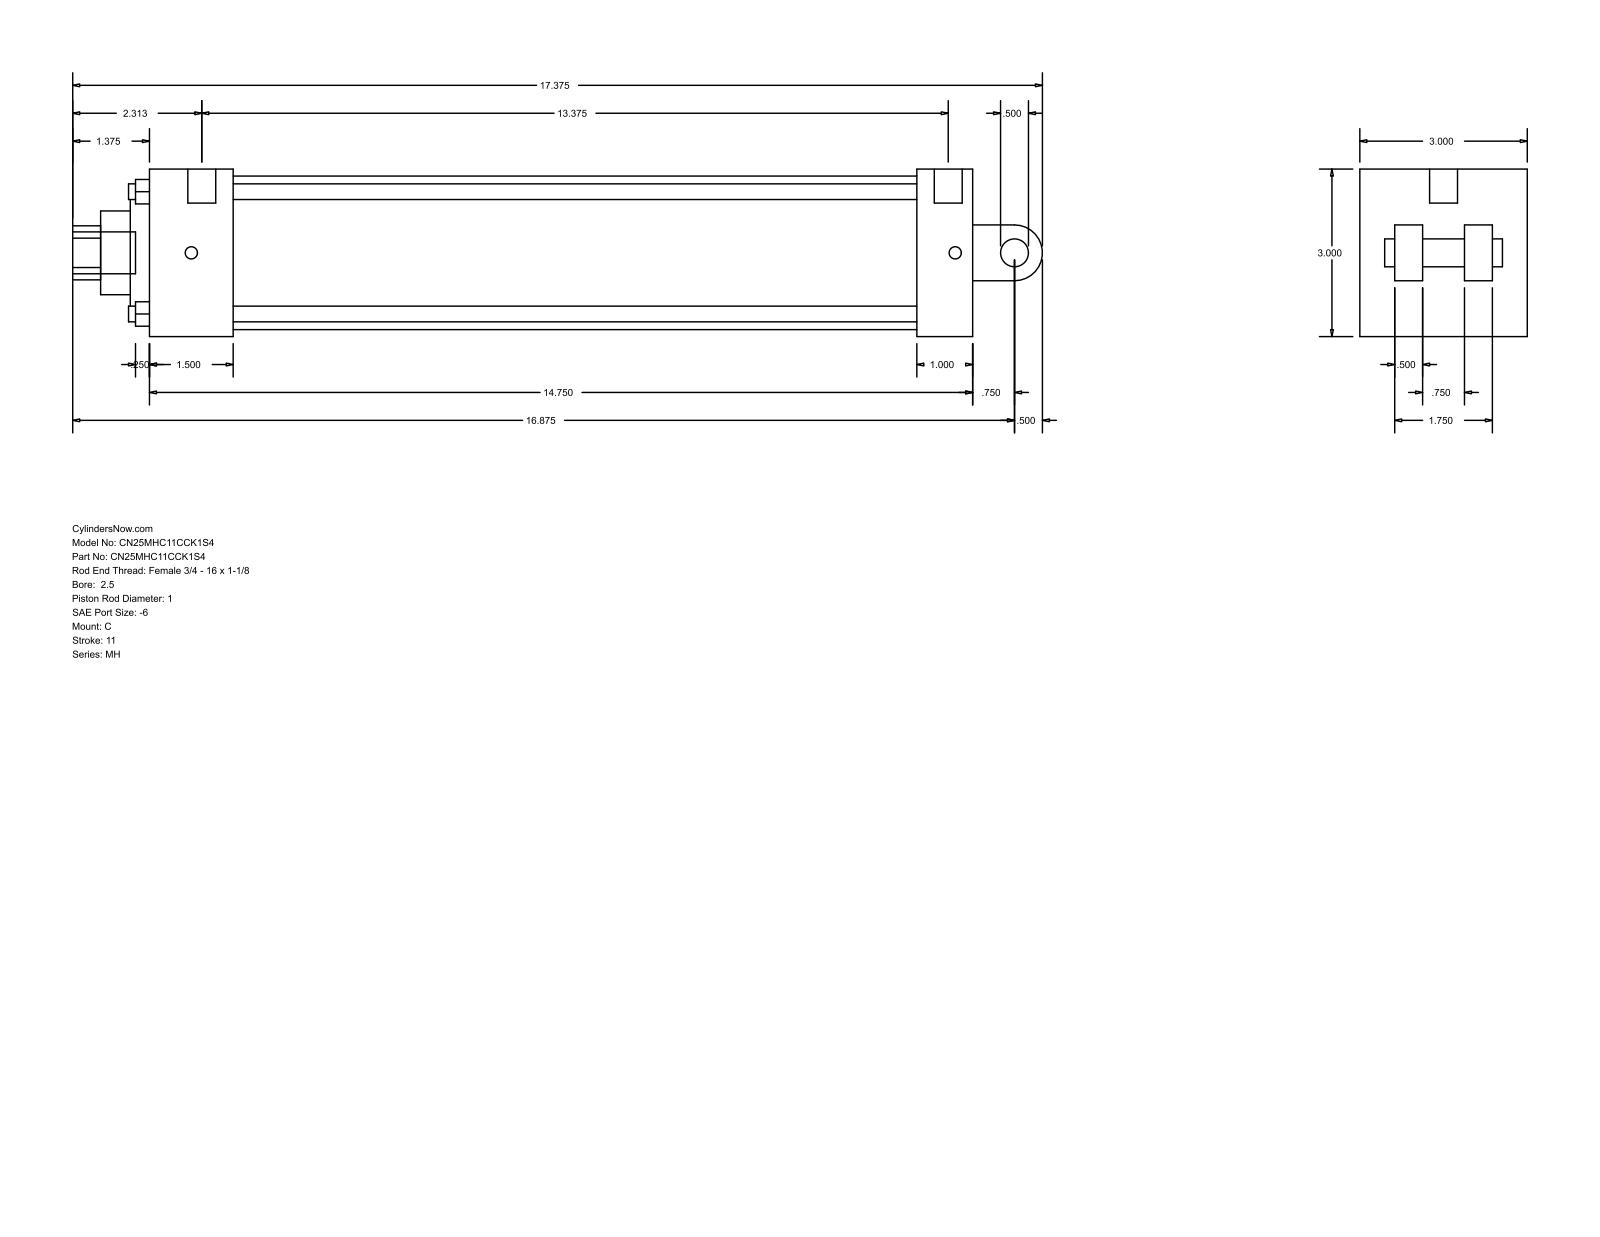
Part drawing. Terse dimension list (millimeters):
name: MH_C__0250_1
written by: GSSL Pune (CONFIG_CONTROL_DESIGN)
unit: mm
bodies: 0 solids, 101 faces (71 planar, 30 cylindrical, 0 other)
size: 441.32 × 76.2 × 76.2
holes: 4× ⌀7.14, 2× ⌀5.56, 1× ⌀12.7, 1× ⌀25.4, 1× ⌀38.1, 1× ⌀60.33, 1× ⌀69.85
bosses: 2× ⌀12.7, 2× ⌀5.56, 1× ⌀19.05
rounds: 1× R12.29, 1× R12.7
face distances: 76.2, 374.65, 15.87, 25.39, 60.33, 349.26, 38.11, 311.15, 336.54, 12.7
hole spacings: 39.33, 55.62, 78.66, 3.18
